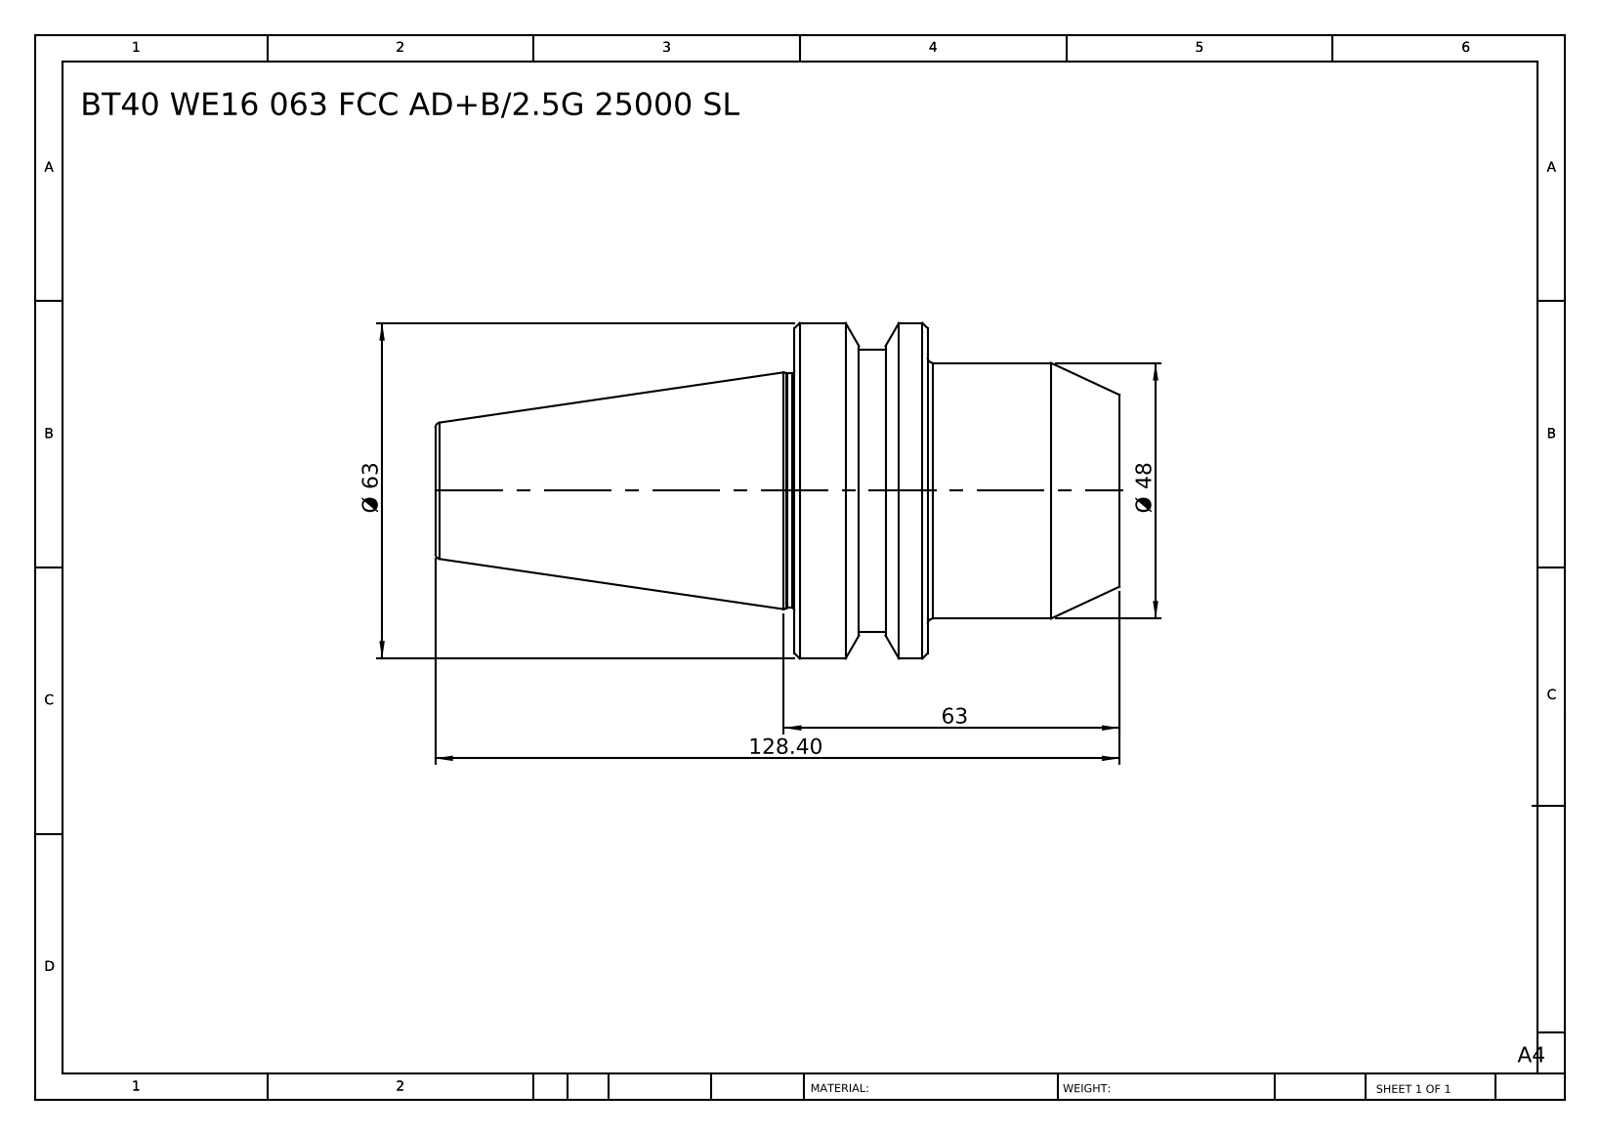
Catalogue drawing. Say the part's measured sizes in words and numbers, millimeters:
The part is named "BT40 WE16 063 AD-6.3G15000 SL". Its 3-D file was written by "SolidWorks 2014 (CONFIG_CONTROL_DESIGN)". It is 1 solid with 38 faces: 6 planar, 10 cylindrical and 22 other. Overall it measures 128.4 by 63 by 63 millimeters. Its volume is 198 188 cubic millimeters and its surface area 22 838 square millimeters. Round bosses or shafts: 1 of diameter 63, 1 of diameter 53, 1 of diameter 48, 1 of diameter 44. The main face-to-face distances are 61, 36, 25, 128.4, 92.4, 67.4, 48.9, 12.9, 12.1, 79.5.
